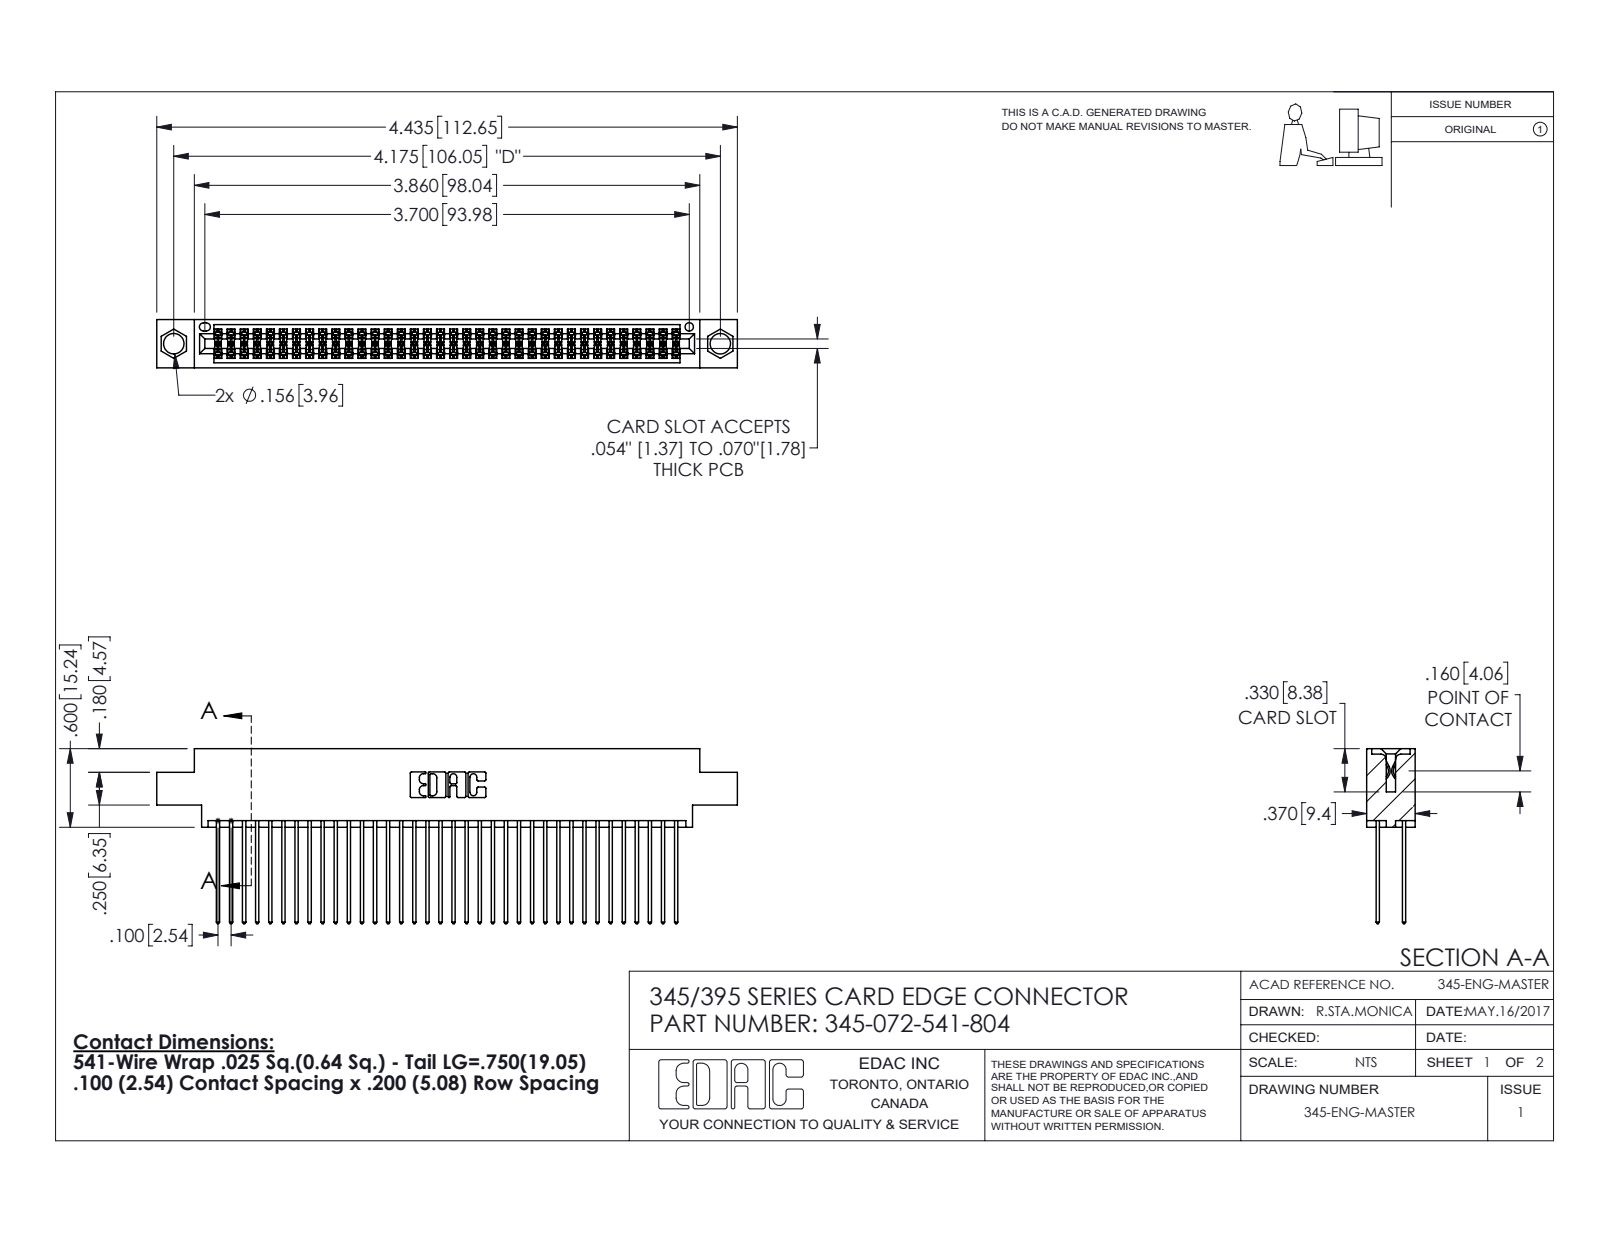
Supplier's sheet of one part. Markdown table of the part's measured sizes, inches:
| quantity | value |
| --- | --- |
| part name | 345-072-541-804; 345-292-001_345-293-141; 345 Part_0.170 Offset - 0.156 Dia-TI |
| STEP written by | SolidWorks 2020 (CONFIG_CONTROL_DESIGN) |
| units | inches |
| bodies | 73 solids, 3744 faces (2474 planar, 1270 cylindrical, 0 other) |
| overall size | 4.435 × 1.337 × 0.37 |
| volume | 0.676 in³ |
| surface area | 28.21 in² |
| round holes (diameter × count) | 0.156 × 2, 0.064 × 1 |
| partial cylindrical surfaces (radius × count) | 0.006 × 108, 0.01 × 72, 0.01 × 22, 0.007 × 6, 0.031 × 6, 0.026 × 3, 0.014 × 2, 0.019 × 2 |
| main face-to-face distances | 0.072, 0.298, 0.2, 0.098, 0.272, 0.025, 0.37, 0.225, 0.175, 0.149 |
| hole center spacings | 0.27, 3.939, 4.175 |
